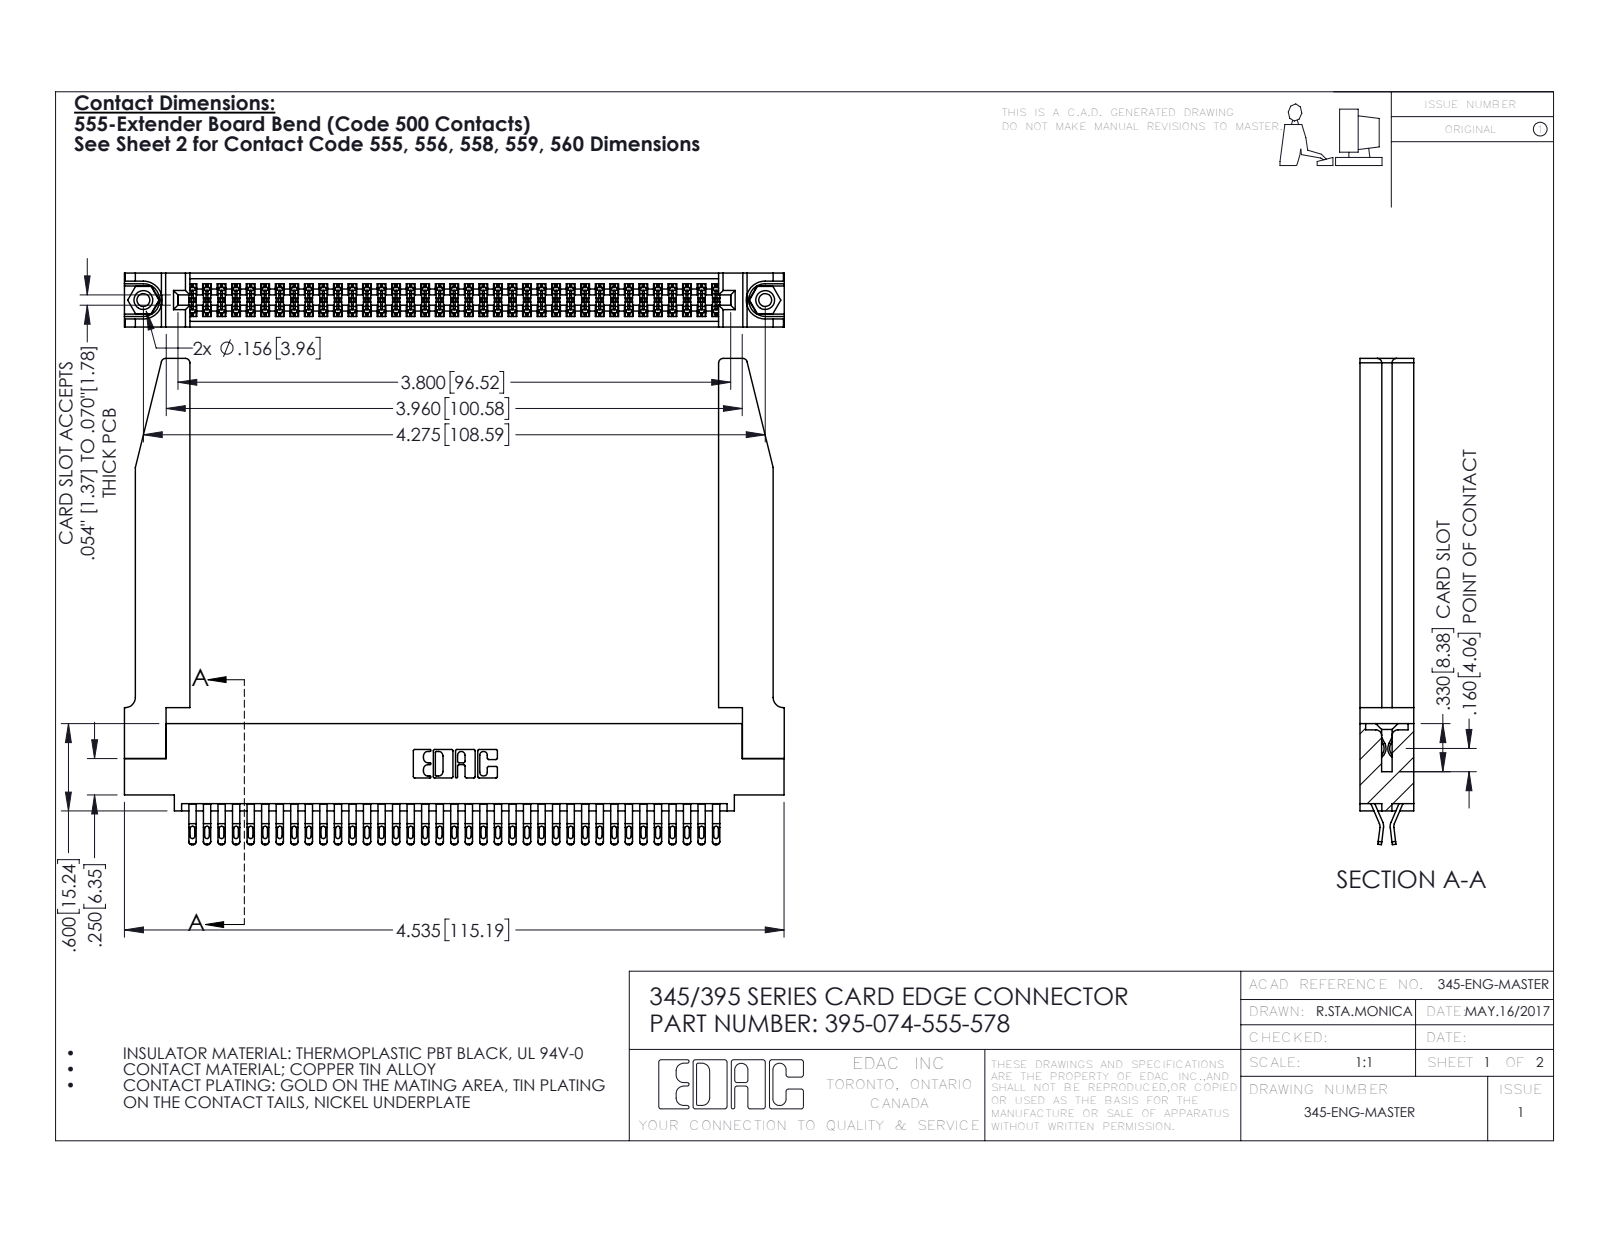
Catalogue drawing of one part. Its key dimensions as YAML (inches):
part_name: "345-292-001_555 Tail; 345-220-078_345-220-078; 395-074-555-578; 345 Part_0.110 Offset - 0.156 Dia-TH (+1 more)"
step_written_by: "SolidWorks 2016 (CONFIG_CONTROL_DESIGN)"
units: inches
bodies: {solids: 79, faces: 4508, planar: 2520, cylindrical: 1936, other: 52}
overall_size: [4.536, 3.342, 0.37]
volume: 1.163
surface_area: 37.61
round_holes:
  - {diameter: 0.089, count: 2}
  - {diameter: 0.125, count: 2}
  - {diameter: 0.156, count: 2}
  - {diameter: 0.064, count: 1}
round_bosses_or_shafts:
  - {diameter: 0.155, count: 2}
partial_cylinders:
  - {radius: 0.016, count: 185}
  - {radius: 0.02, count: 148}
  - {radius: 0.006, count: 111}
  - {radius: 0.01, count: 22}
  - {radius: 0.03, count: 8}
  - {radius: 0.007, count: 6}
  - {radius: 0.031, count: 6}
  - {radius: 0.026, count: 3}
face_to_face_distances: [0.37, 0.072, 0.298, 0.025, 0.098, 0.272, 0.2, 0.225, 0.15, 0.148]
hole_center_spacings: [0.27, 4.039, 4.275]
